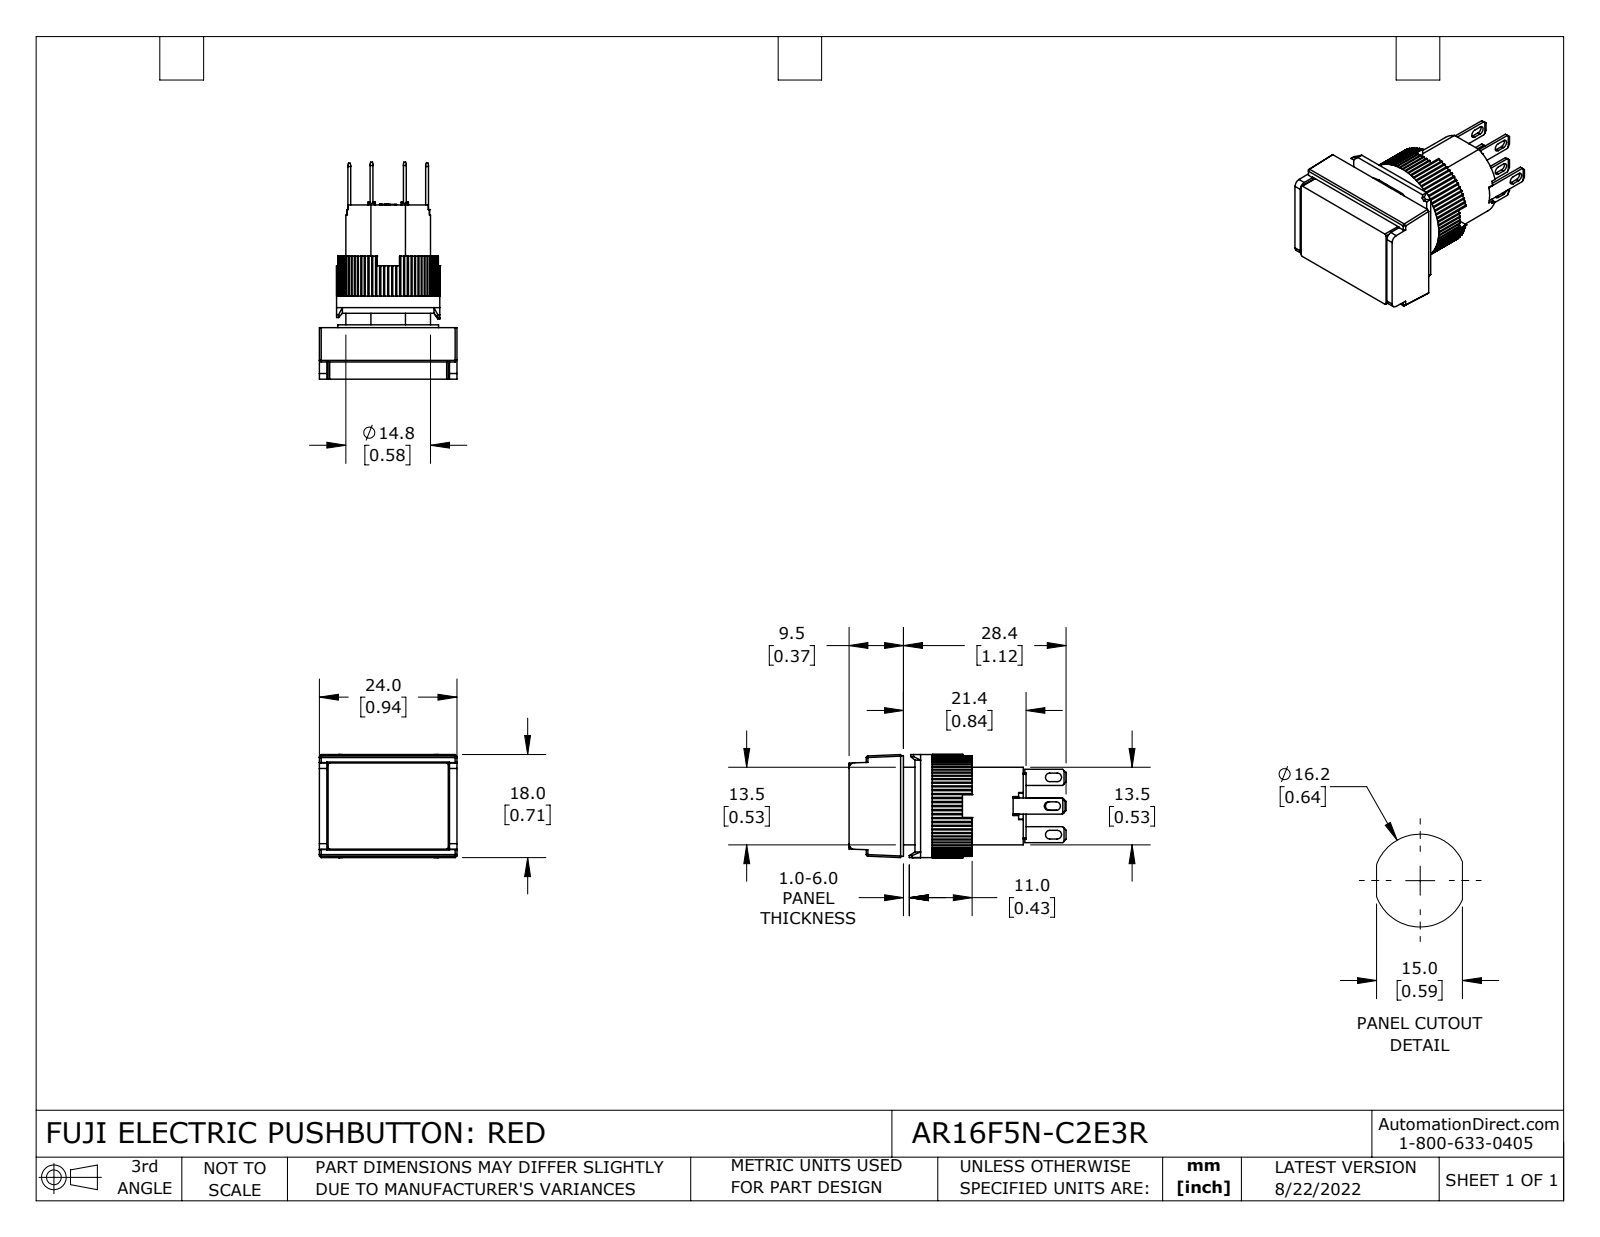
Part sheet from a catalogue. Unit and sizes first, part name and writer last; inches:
Units: inches
Overall size (bounding box): 1.492 × 0.945 × 0.709
Round holes (diameter × count): ⌀0.543 ×1, ⌀0.583 ×1
Round bosses / shafts (diameter × count): ⌀0.709 ×1, ⌀0.693 ×1
Partial cylindrical surfaces — rounded edges, fillets, slot ends (radius × count): R0.01 ×80, R0.008 ×12, R0.03 ×8, R0.012 ×6, R0.039 ×2
Main face-to-face distances: 0.213, 0.354, 0.142, 0.35, 0.492, 0.138, 0.02, 0.843, 0.059, 0.453
Volume: 0.444 in³ · Surface area: 9.306 in²
Bodies: 14 solids, 843 faces (656 planar, 183 cylindrical, 4 other)
Part name (STEP PRODUCT): AR16F5N-C2E3R
STEP written by: SolidWorks 2021 (CONFIG_CONTROL_DESIGN)
